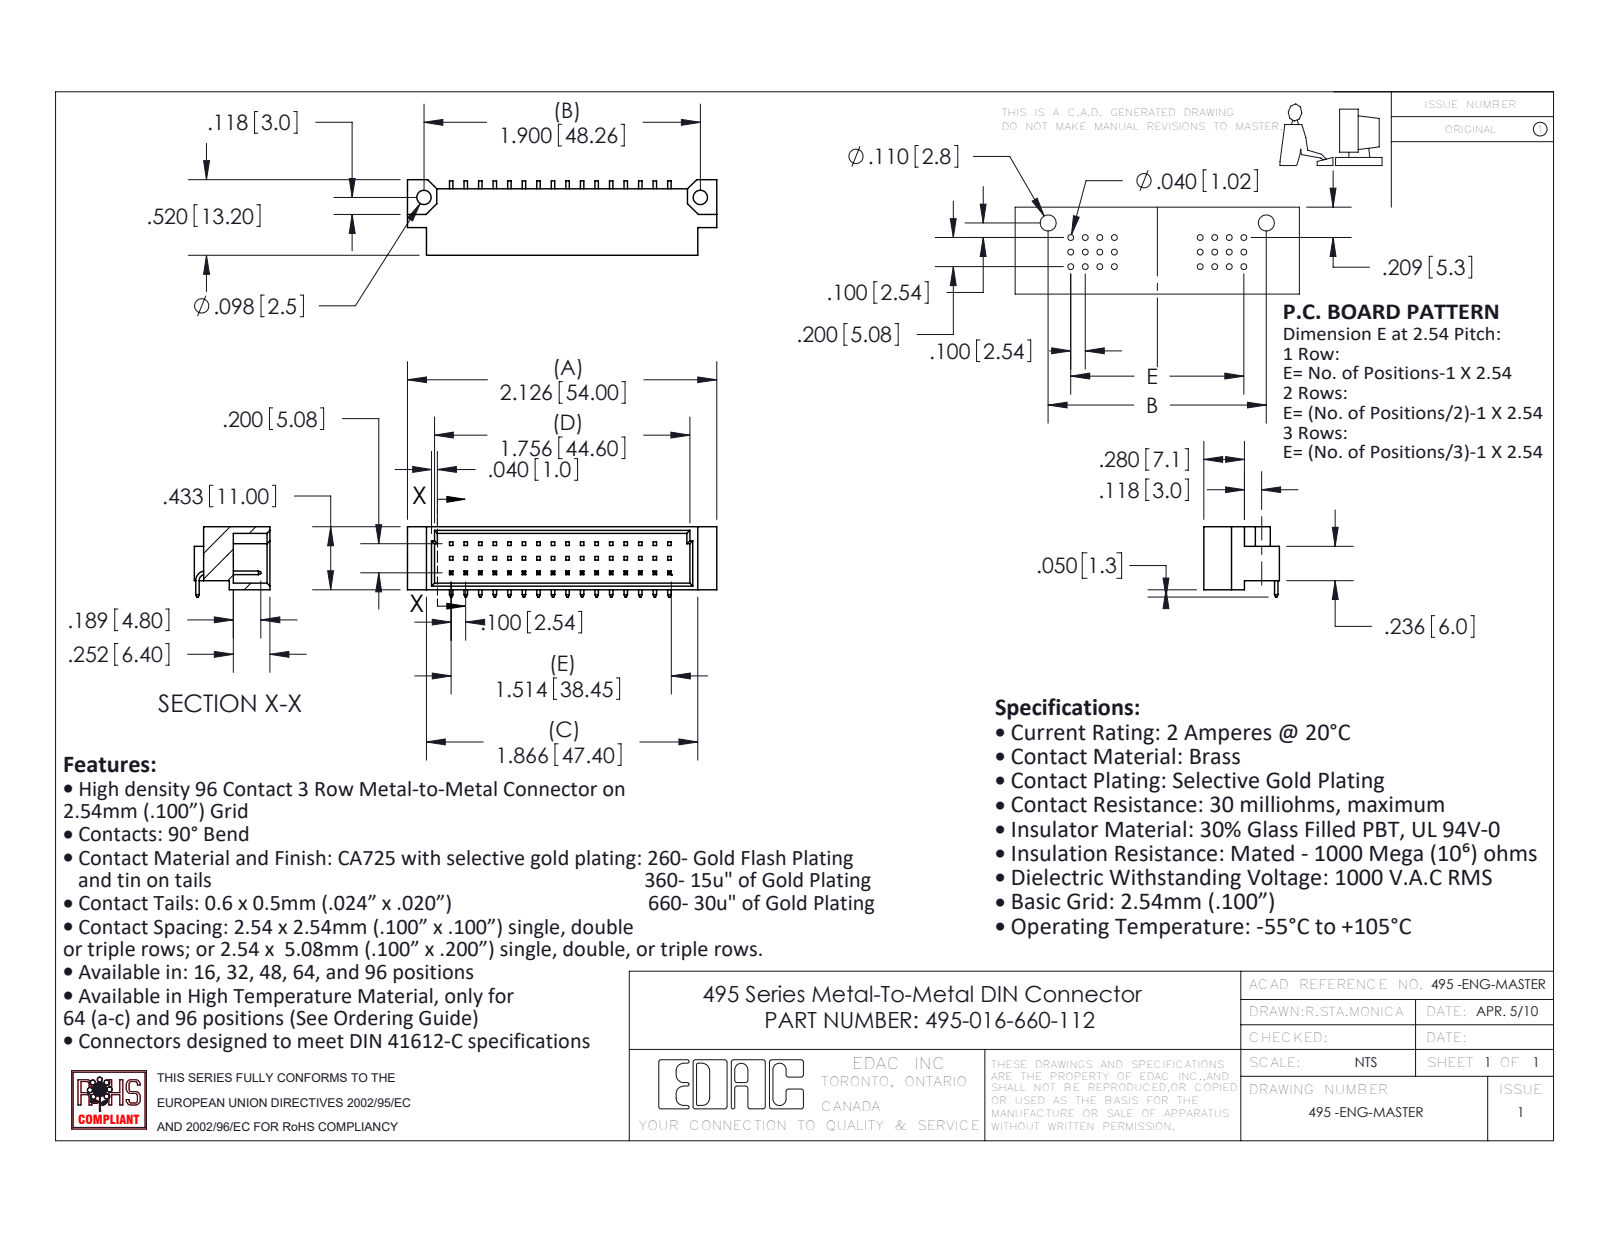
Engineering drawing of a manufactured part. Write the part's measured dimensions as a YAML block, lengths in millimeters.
part_name: "495-016-660-112; 495-290-3; 495 Part_48"
step_written_by: "SolidWorks 2020 (AUTOMOTIVE_DESIGN)"
units: millimeters
bodies: {solids: 17, faces: 530, planar: 494, cylindrical: 36, other: 0}
overall_size: [54, 13.2, 12.27]
volume: 3535
surface_area: 4531
round_holes:
  - {diameter: 2.49, count: 2}
partial_cylinders:
  - {radius: 1.02, count: 1}
  - {radius: 1.65, count: 1}
face_to_face_distances: [1.14, 9.86, 5.2, 2.54, 11, 1.6, 5.08, 0.61, 8.72, 9.4]
hole_center_spacings: [48.26]
